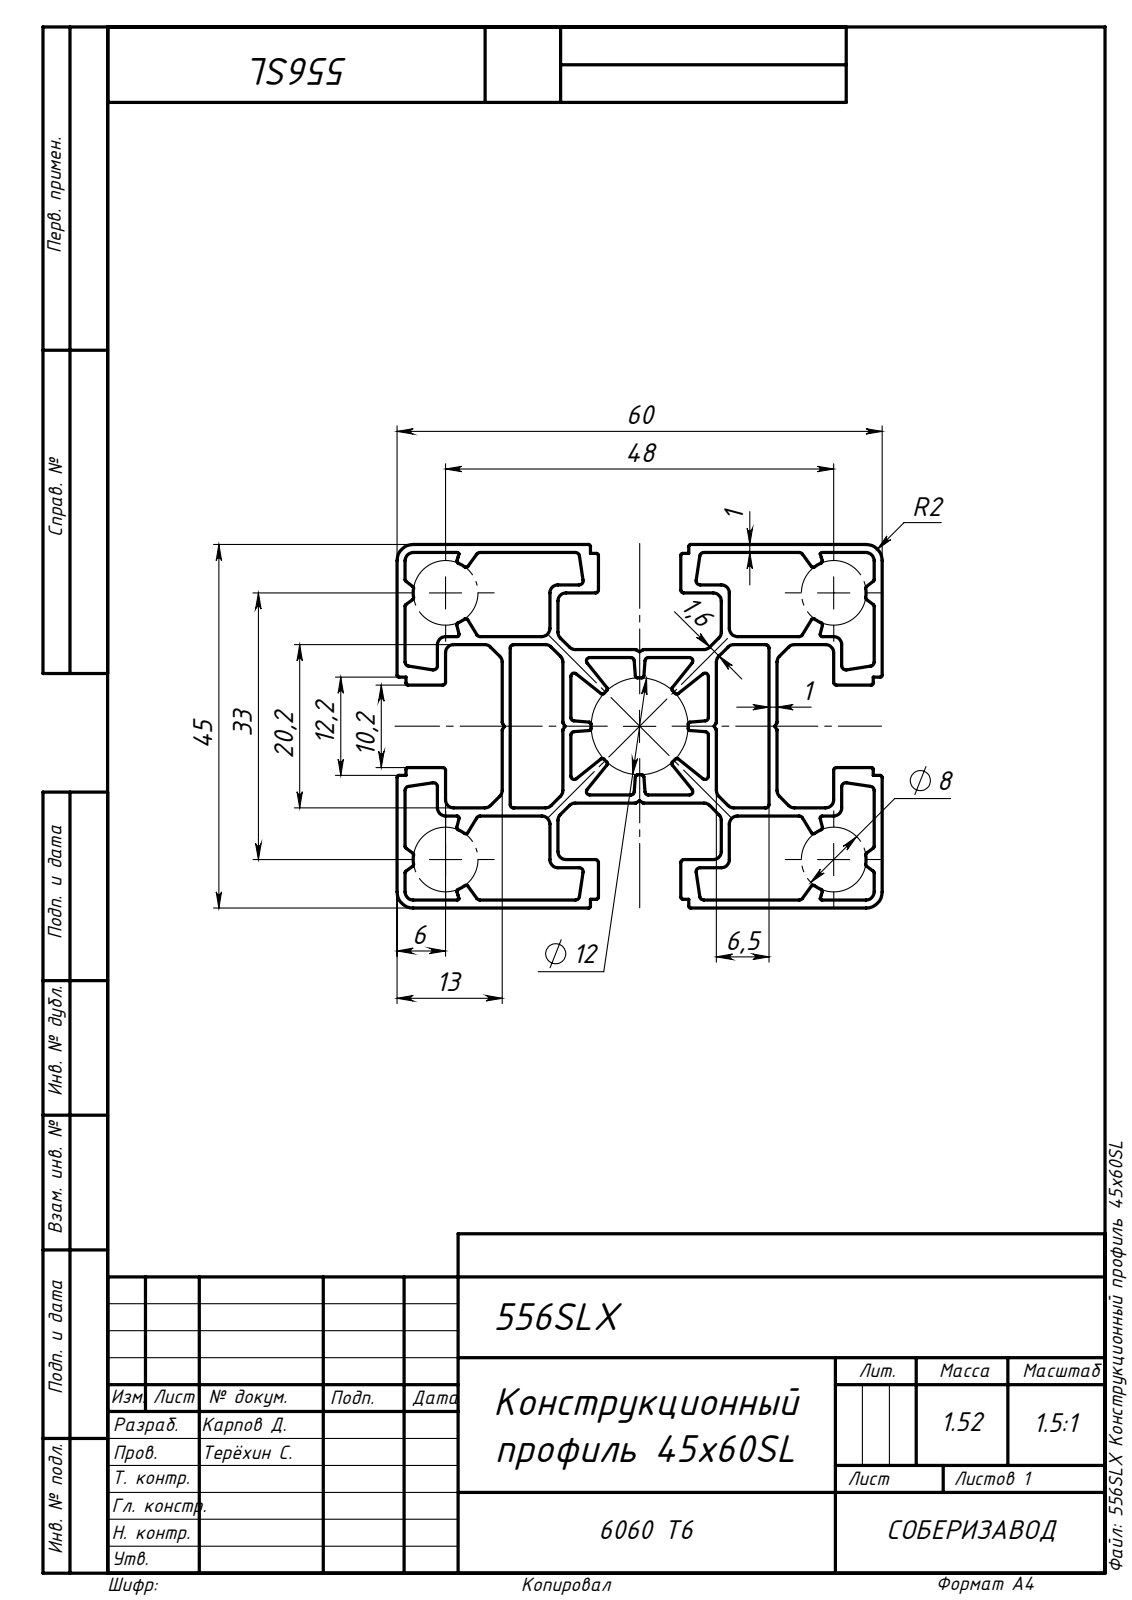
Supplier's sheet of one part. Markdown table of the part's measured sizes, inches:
| quantity | value |
| --- | --- |
| STEP written by | SolidWorks 2019 (AUTOMOTIVE_DESIGN) |
| units | inches |
| bodies | 1 solid, 424 faces (192 planar, 232 cylindrical, 0 other) |
| overall size | 39.37 × 2.362 × 1.772 |
| volume | 34.27 in³ |
| surface area | 1 386 in² |
| partial cylindrical surfaces (radius × count) | 0.01 × 84, 0.039 × 52, 0.02 × 24, 0.016 × 20, 0.014 × 8, 0.079 × 8, 0.157 × 4 |
| main face-to-face distances | 0.039, 0.512, 0.063, 0.772, 0.449, 1.772, 0.197, 1.732, 1.811, 1.283 |
